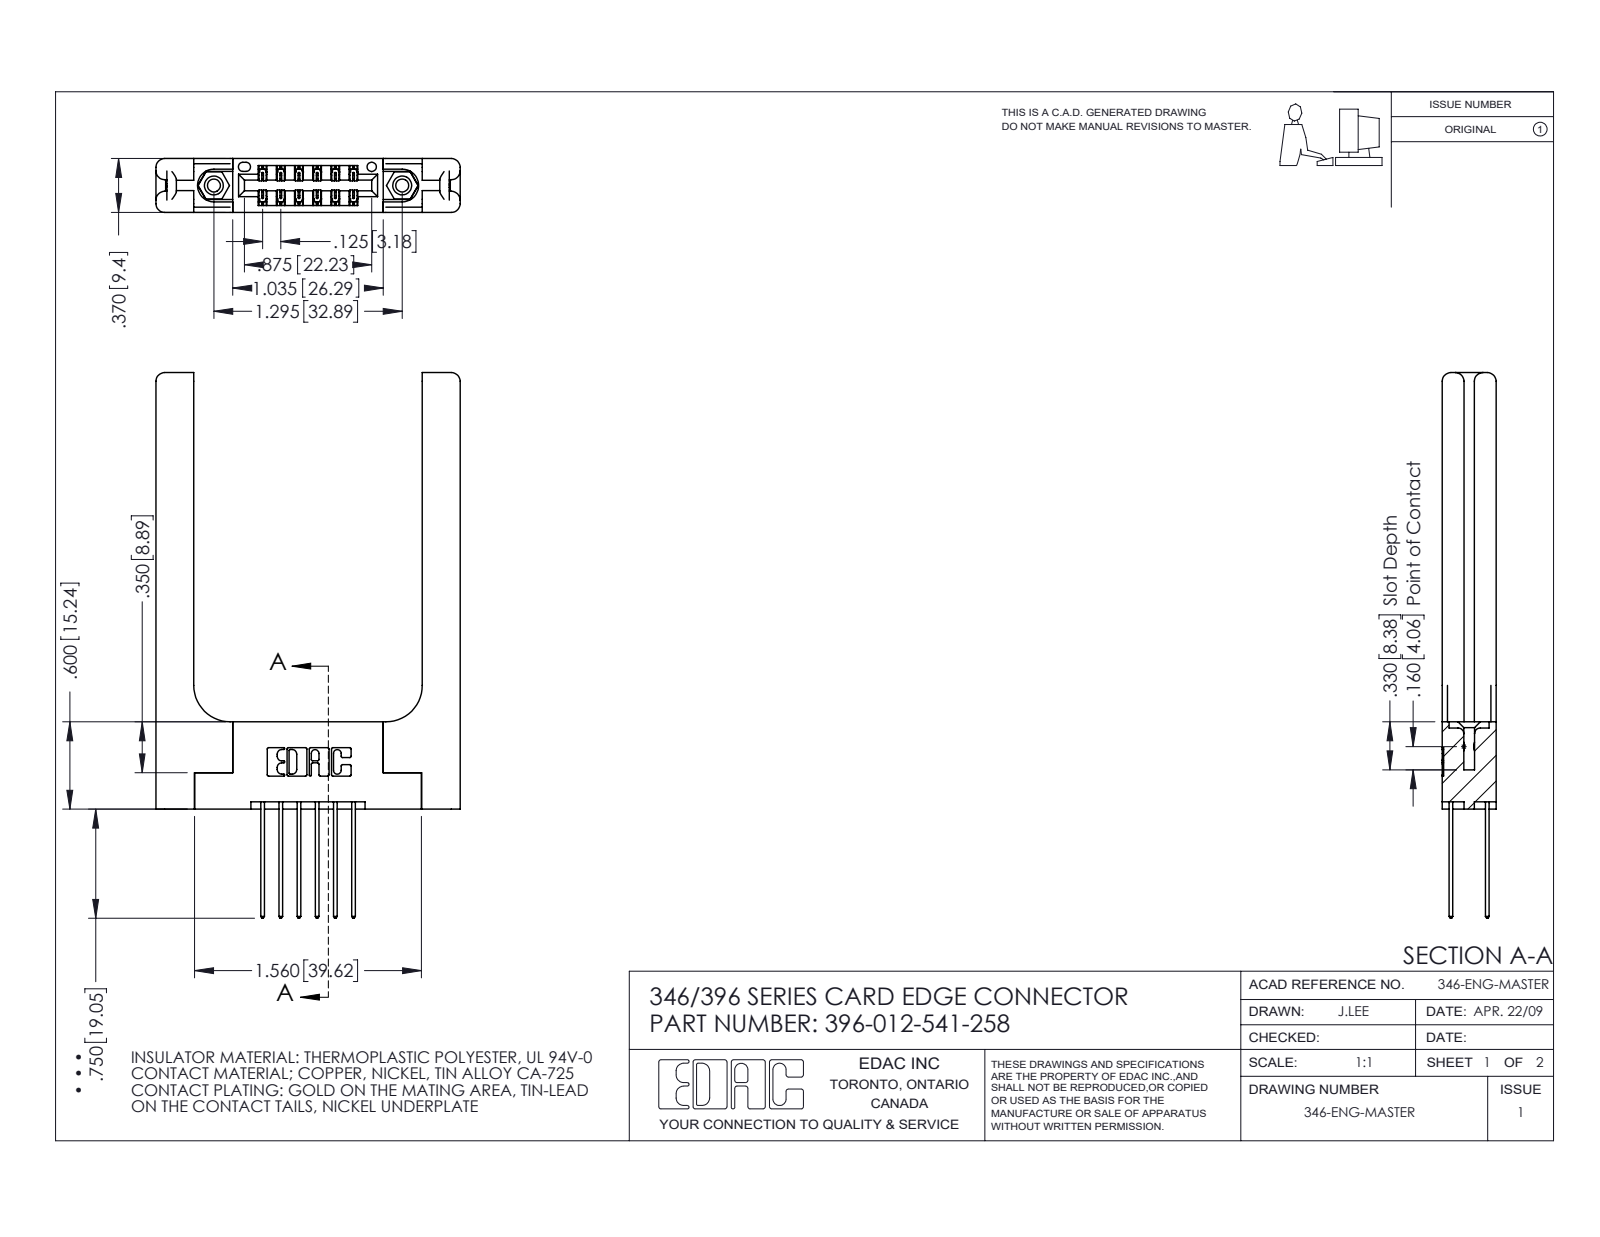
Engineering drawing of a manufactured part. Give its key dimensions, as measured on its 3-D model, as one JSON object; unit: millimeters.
{"part_name": "345-292-001_345-293-141; 345-250-001_345-250-001-102; 346-220-058_345-220-058; 346 Part_Flush Mounting Lugs - 0.156 Dia-TH (+1 more)", "step_written_by": "SolidWorks 2016 (CONFIG_CONTROL_DESIGN)", "units": "millimeters", "bodies": {"solids": 17, "faces": 1002, "planar": 644, "cylindrical": 298, "other": 60}, "overall_size": [95.3, 53.1, 9.4], "volume_mm3": 12500, "surface_area_mm2": 11570, "round_holes": [[2.3, 2], [3.2, 2], [4, 2], [1.6, 1]], "round_bosses_or_shafts": [[3.9, 2]], "partial_cylinders_radius": [[0.3, 22], [0.2, 18], [1.5, 16], [0.3, 12], [0.2, 6], [0.8, 6], [0.7, 3], [0.4, 2]], "face_to_face_distances": [9.4, 3.8, 5.6, 6.4, 1.8, 3.8, 2.6, 1.2, 8.2, 4.4], "hole_center_spacings": [6.2, 27.7, 32.9]}
